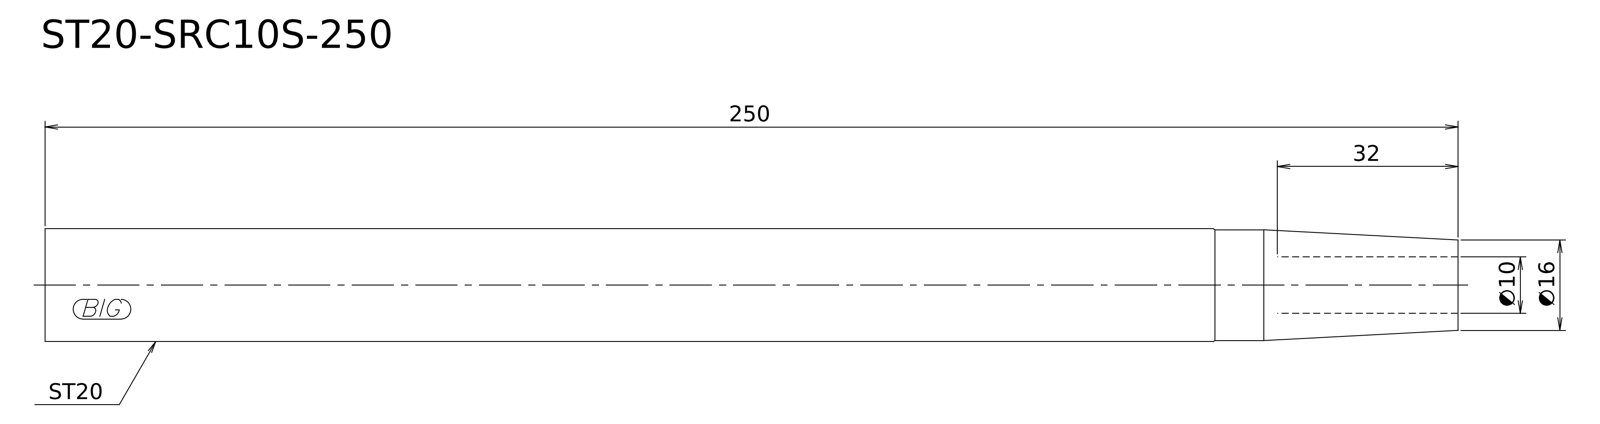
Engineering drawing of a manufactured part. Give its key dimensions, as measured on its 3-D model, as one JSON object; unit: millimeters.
{"step_written_by": "Kubotek KeyCreator V8.5.1 (14335) (CONFIG_CONTROL_DESIGN)", "units": "millimeters", "bodies": {"solids": 1, "faces": 6, "planar": 2, "cylindrical": 2, "other": 2}, "overall_size": [250, 20, 20], "volume_mm3": 76216, "surface_area_mm2": 15981, "round_bosses_or_shafts": [[20, 1], [19.6, 1]], "face_to_face_distances": [250]}
